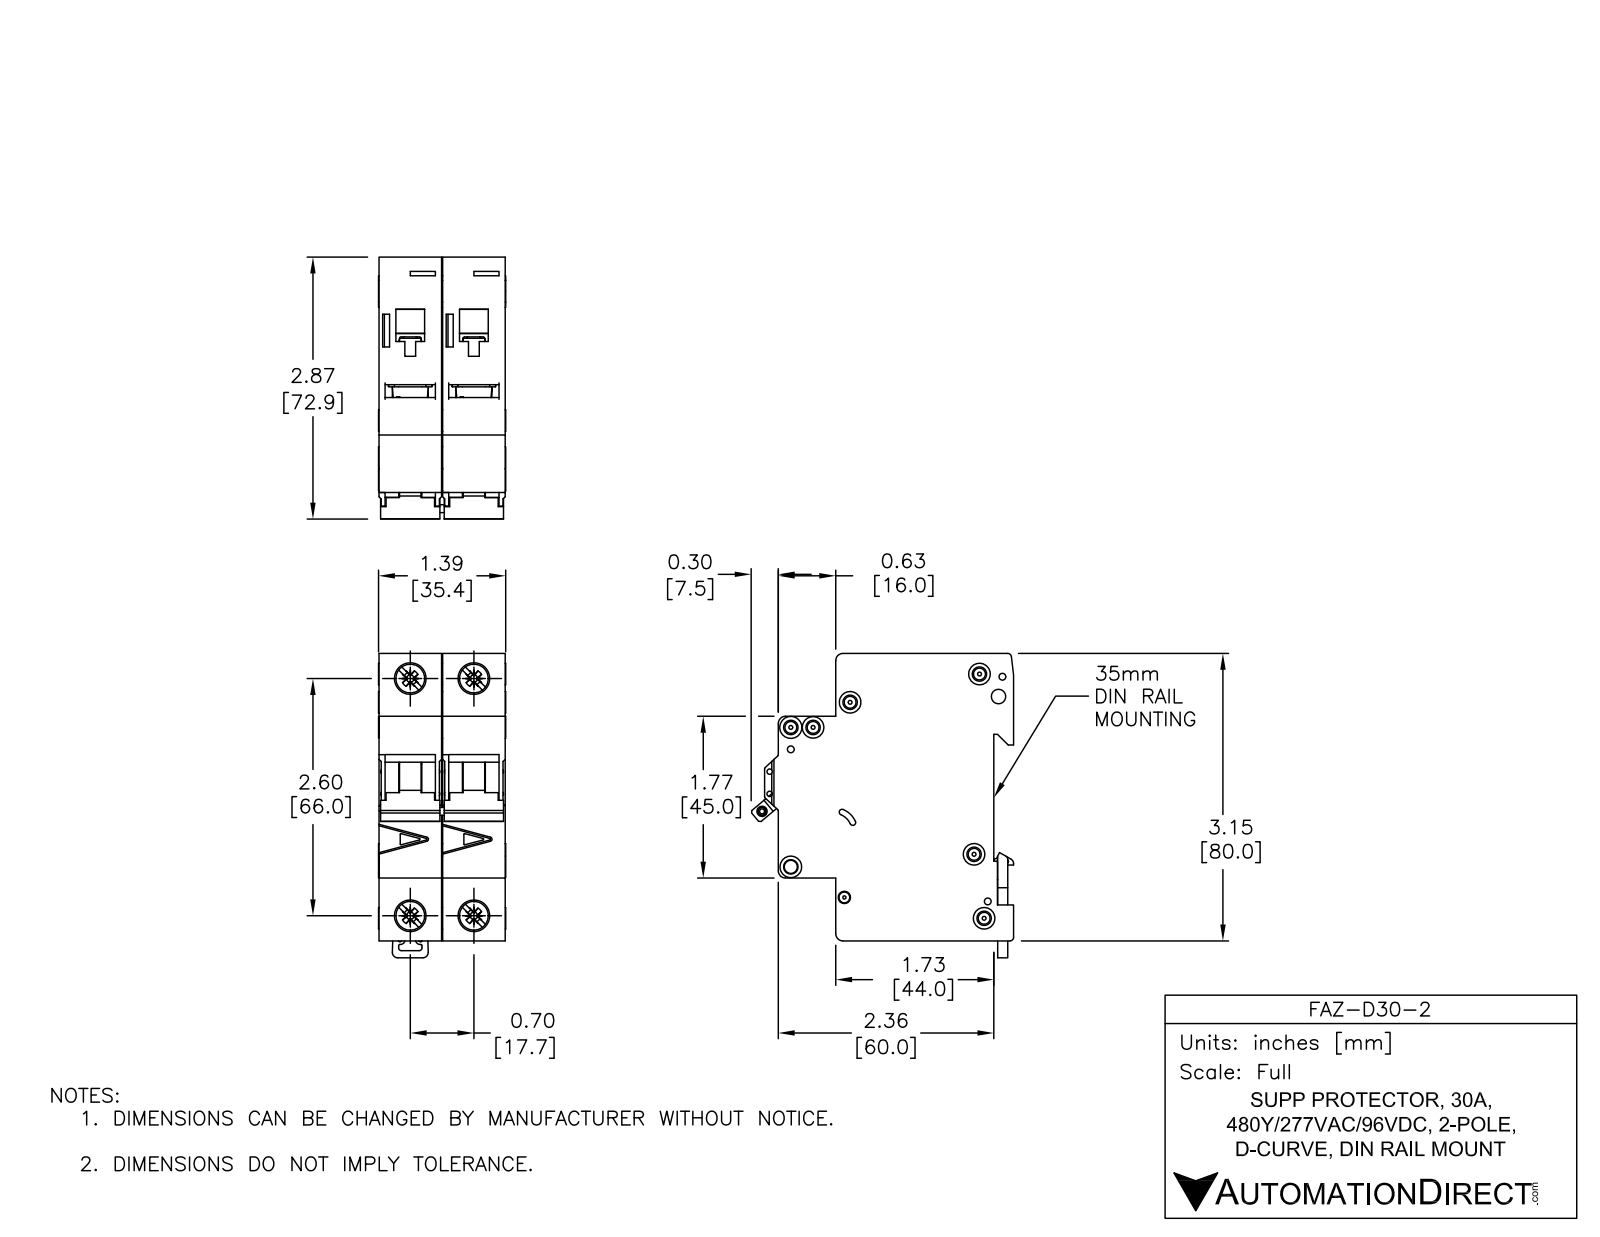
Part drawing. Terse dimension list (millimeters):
name: FAZ-D30-2
written by: SolidWorks 2014 (AUTOMOTIVE_DESIGN)
unit: mm
bodies: 8 solids, 1104 faces (466 planar, 396 cylindrical, 242 other)
size: 84.78 × 73.04 × 35.4
volume: 149 808 mm³; area: 38 799 mm²
holes: 6× ⌀3.6, 3× ⌀1.9, 2× ⌀1.09, 2× ⌀1.5, 2× ⌀4, 2× ⌀7.15, 2× ⌀8.2, 1× ⌀2.15, 1× ⌀2.2, 1× ⌀2.55, 1× ⌀3.3, 1× ⌀3.4
bosses: 4× ⌀6, 2× ⌀8.2, 2× ⌀2.5
rounds: 49× R0.25, 19× R0.5, 10× R2, 8× R0.2, 8× R1, 2× R0.8, 2× R1.8, 2× R3
face distances: 17.7, 17.5, 35.2, 79.48, 5.5, 49.5, 44, 65.5, 60, 16
hole spacings: 6.2, 13.64, 17.7, 66, 68.33, 4.81, 5.19, 5.61
